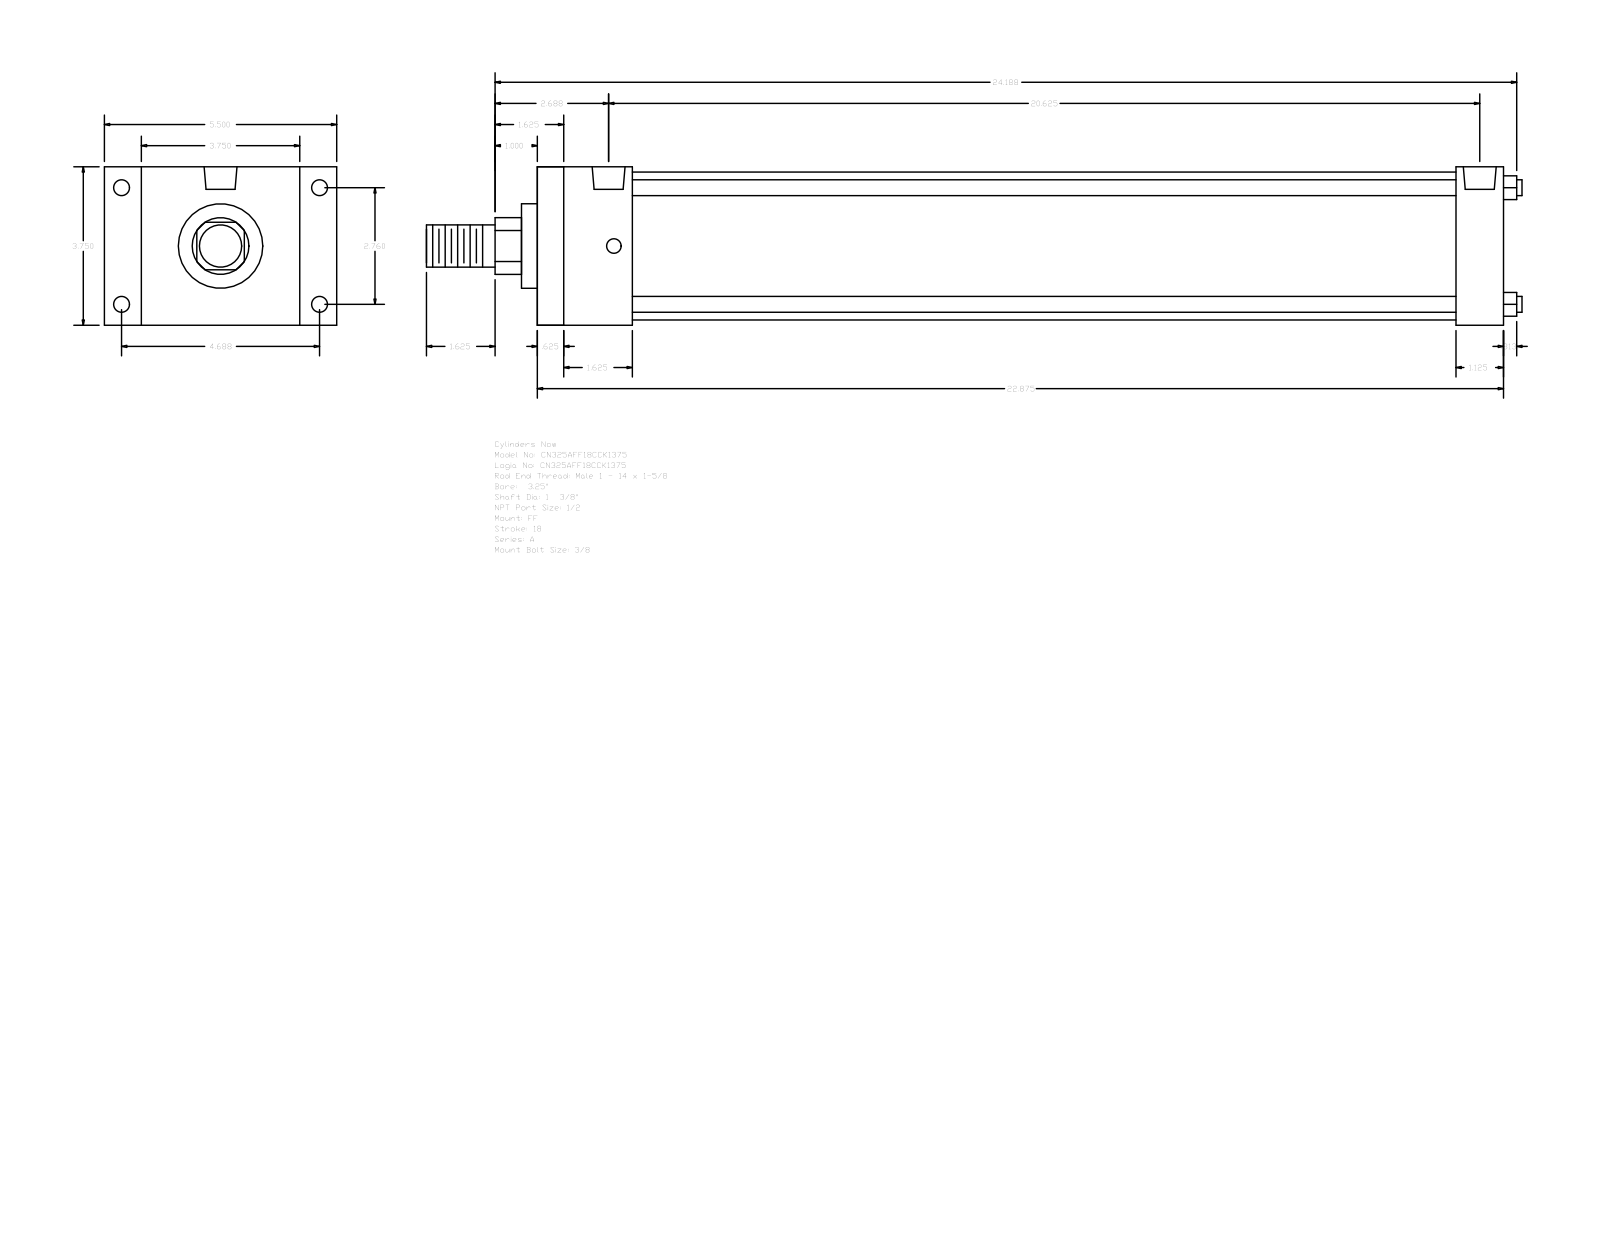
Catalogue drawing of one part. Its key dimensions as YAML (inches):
part_name: "A_FF__0325_1.375"
step_written_by: "GSSL Pune (CONFIG_CONTROL_DESIGN)"
units: inches
bodies: {solids: 0, faces: 92, planar: 64, cylindrical: 28, other: 0}
overall_size: [25.937, 5.5, 3.75]
round_holes:
  - {diameter: 0.344, count: 4}
  - {diameter: 0.375, count: 4}
  - {diameter: 0.778, count: 2}
round_bosses_or_shafts:
  - {diameter: 0.375, count: 4}
  - {diameter: 3.5, count: 1}
  - {diameter: 2, count: 1}
  - {diameter: 1.375, count: 1}
  - {diameter: 1, count: 1}
partial_cylinders:
  - {radius: 0.672, count: 1}
face_to_face_distances: [3.75, 22.875, 22.25, 0.625, 2.25, 0.875, 4.625, 1.125, 21.75, 1.625]
hole_center_spacings: [0.125, 2.76, 4.687, 5.439, 20.375, 20.5, 20.625]
